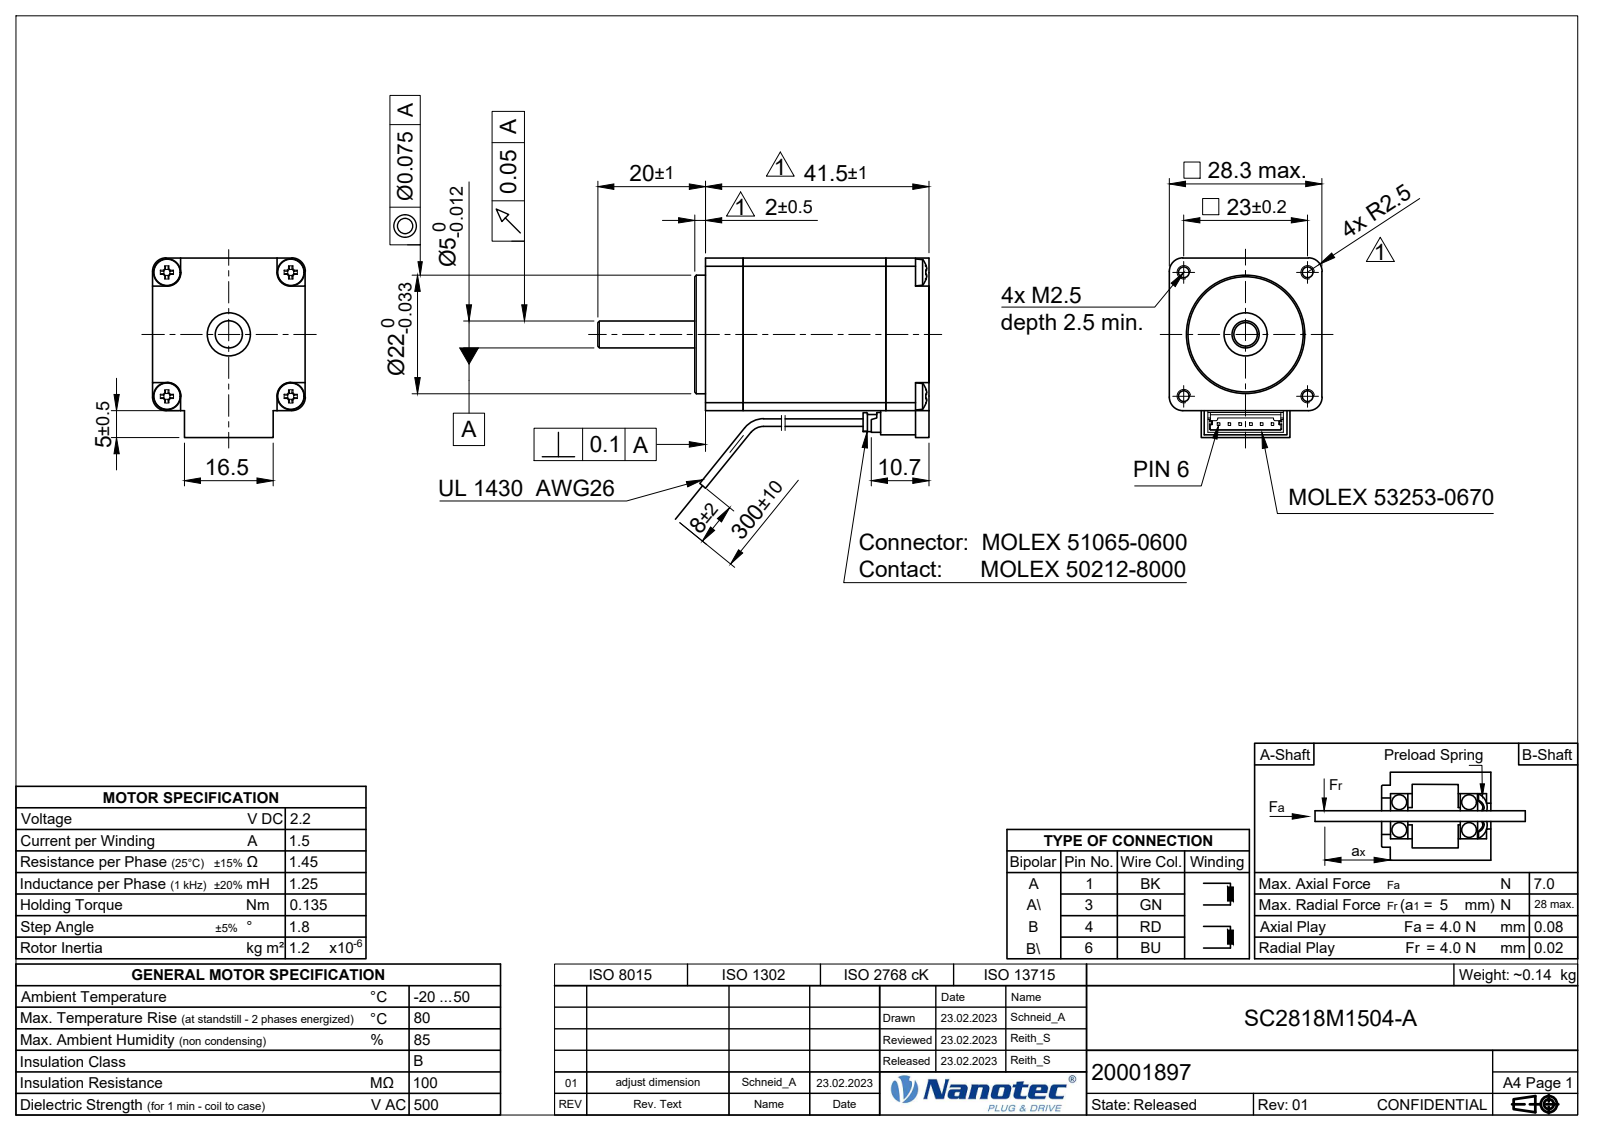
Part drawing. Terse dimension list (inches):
name: PLACEHOLDER
written by: Autodesk Inventor 2021 (AUTOMOTIVE_DESIGN)
unit: in
bodies: 15 solids, 707 faces (567 planar, 52 cylindrical, 88 other)
size: 2.421 × 1.311 × 1.114
volume: 2.108 in³; area: 20.73 in²
holes: 4× ⌀0.079, 1× ⌀0.197, 1× ⌀0.315
bosses: 4× ⌀0.098, 4× ⌀0.089, 4× ⌀0.059, 1× ⌀0.866
rounds: 8× R0.098, 3× R0.008, 2× R0.01, 2× R0.03
face distances: 1.114, 1.043, 0.315, 1.358, 0.276, 1.319, 1.634, 0.079, 0.02, 0.354
hole spacings: 0.64, 0.906, 1.281
